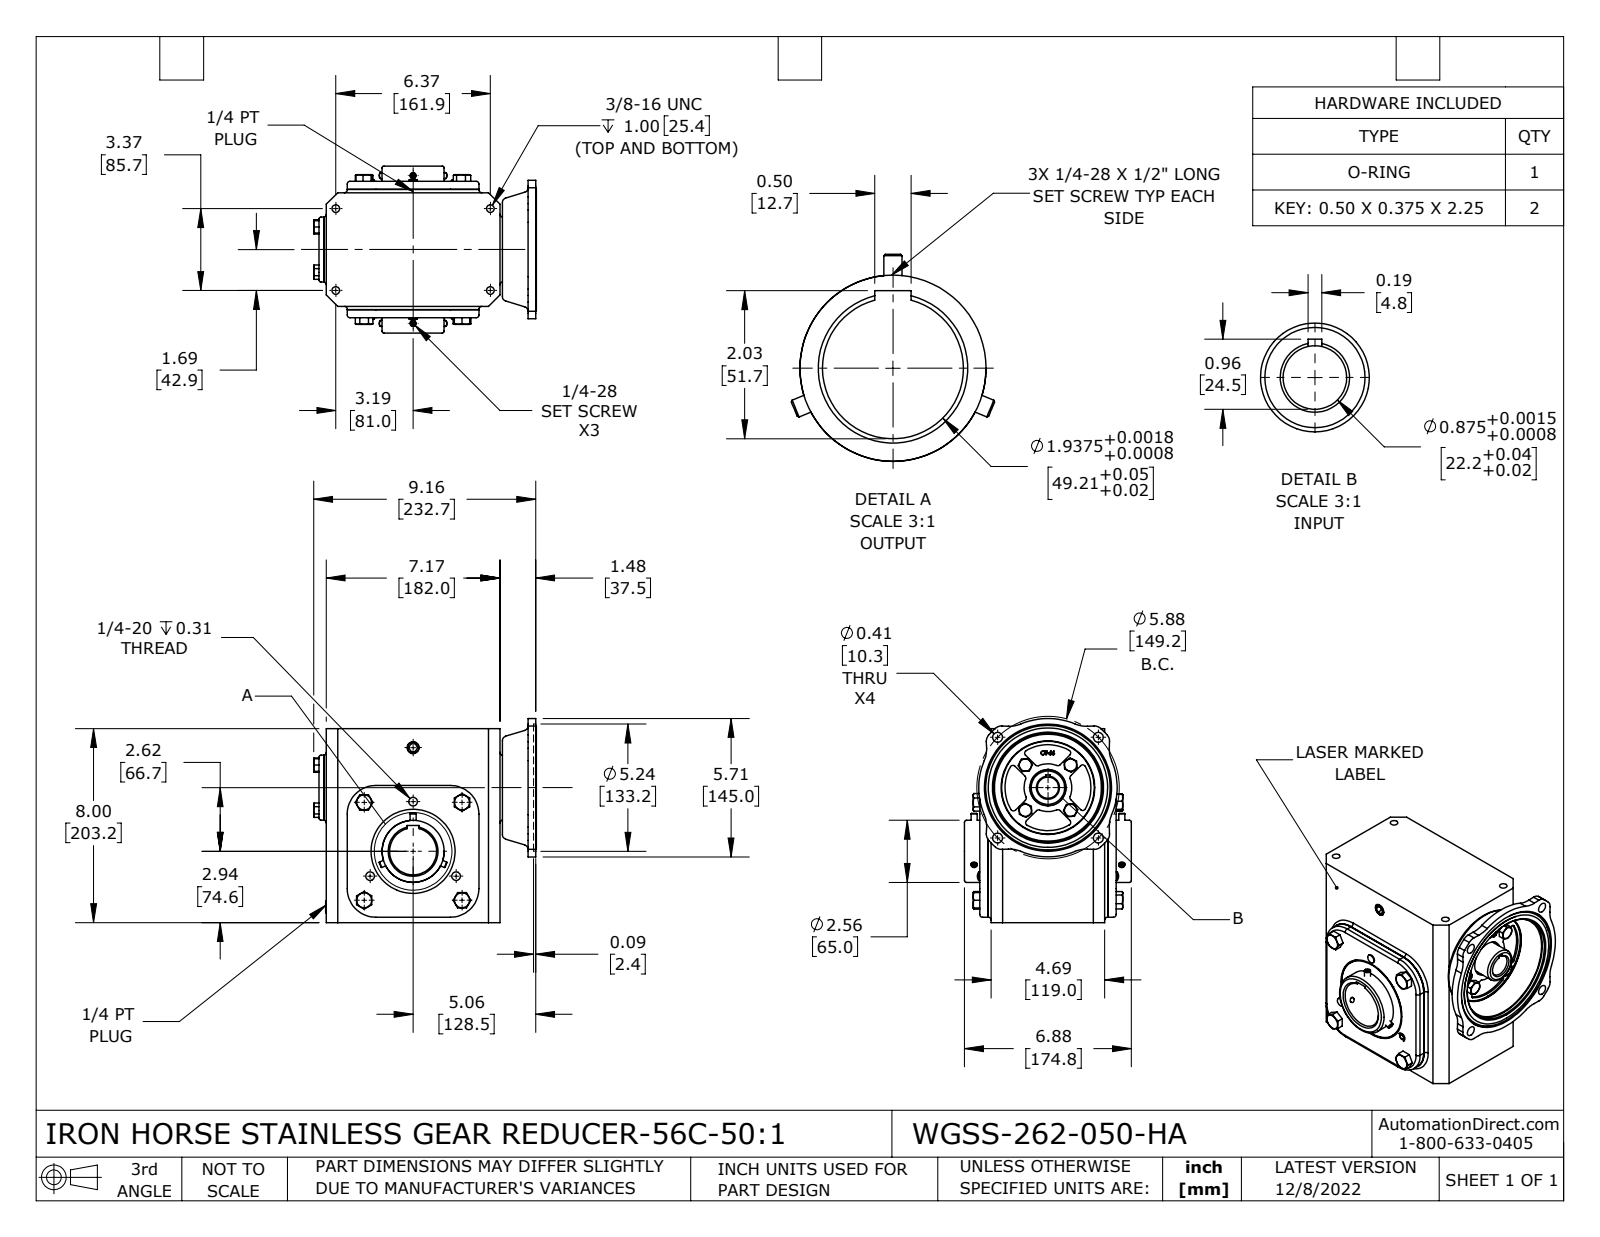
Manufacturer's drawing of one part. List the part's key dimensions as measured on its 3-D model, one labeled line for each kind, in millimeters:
Part name (STEP PRODUCT): WGSS-262-050-HA
STEP written by: SolidWorks 2021 (CONFIG_CONTROL_DESIGN)
Units: millimetres
Bodies: 45 solids, 1776 faces (625 planar, 516 cylindrical, 635 other)
Overall size (bounding box): 233.3 × 213.8 × 174.8
Volume: 1 996 000 mm³ · Surface area: 680 600 mm²
Round holes (diameter × count): ⌀5.4 ×6, ⌀6.8 ×4, ⌀8 ×4, ⌀8.5 ×4, ⌀9 ×4, ⌀10.3 ×4, ⌀11 ×4, ⌀5.1 ×3, ⌀2 ×2, ⌀22.2 ×1, ⌀23.9 ×1, ⌀28 ×1
Round bosses / shafts (diameter × count): ⌀6.4 ×6, ⌀18 ×4, ⌀10 ×4, ⌀8 ×4, ⌀9 ×3, ⌀5.2 ×3, ⌀125 ×1, ⌀112 ×1
Partial cylindrical surfaces — rounded edges, fillets, slot ends (radius × count): R3 ×40, R10 ×12, R30 ×12, R1 ×8, R5 ×8, R2 ×6, R6 ×4, R0.5 ×2
Main face-to-face distances: 5, 8.5, 126, 17, 198.2, 12, 131, 114, 3.5, 177
Hole centre spacings: 81.8, 33.5, 41.1, 47.4, 72.5, 74.6, 88, 102.5
